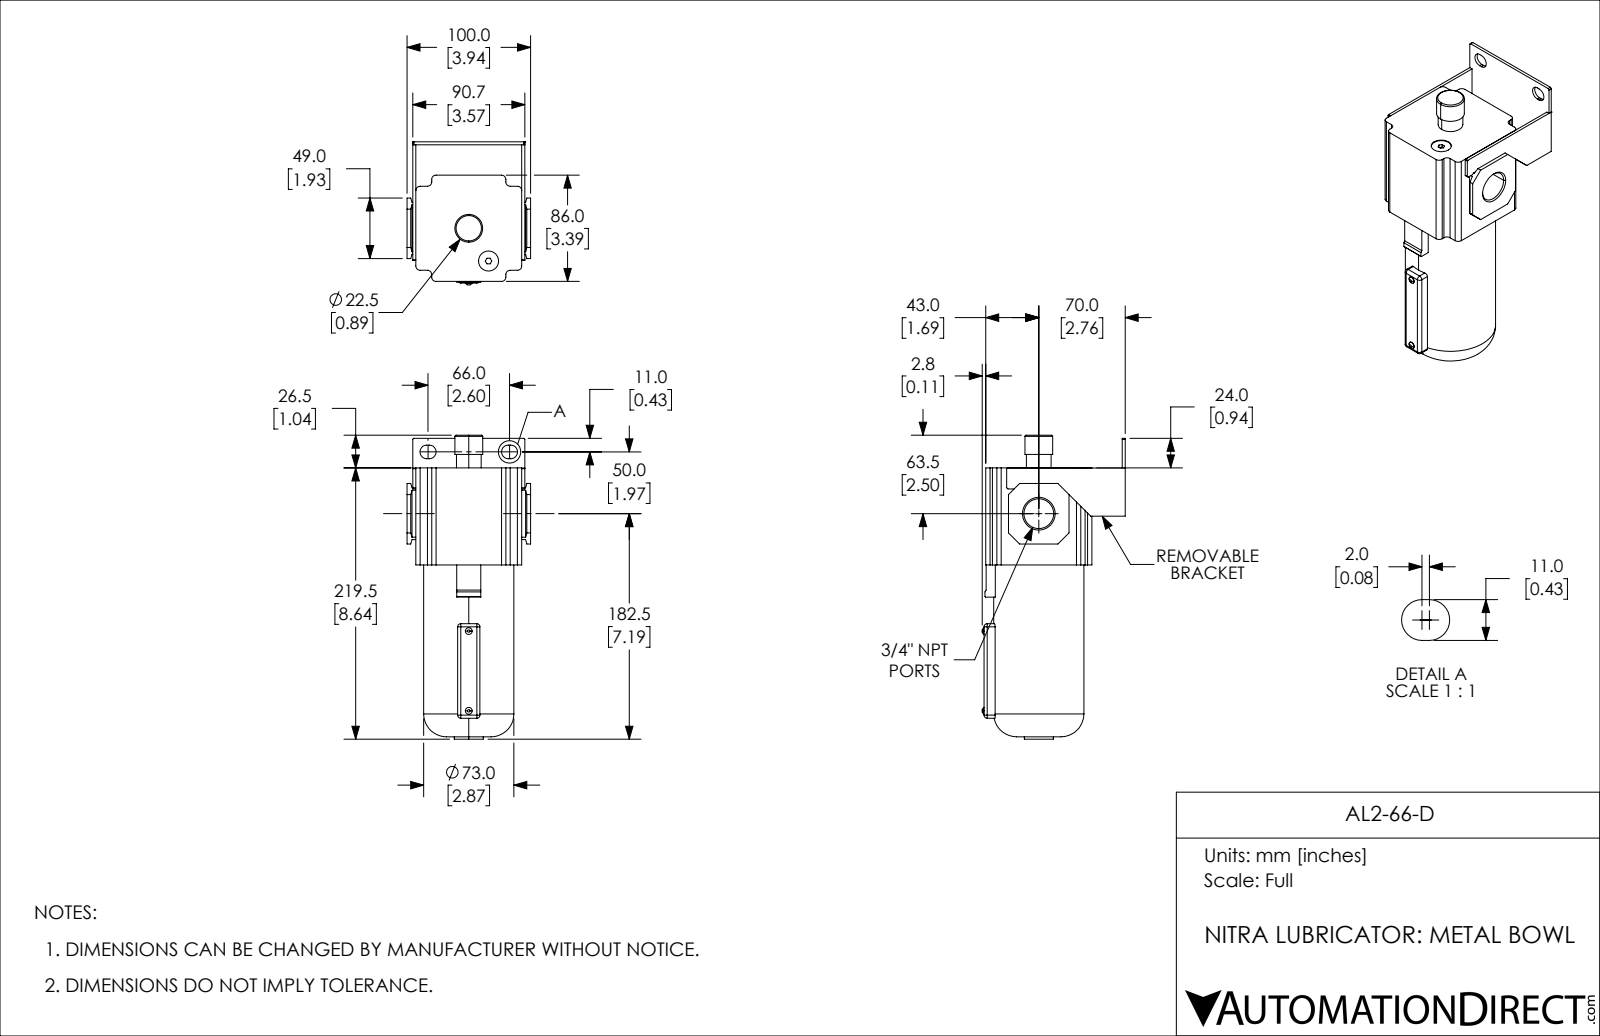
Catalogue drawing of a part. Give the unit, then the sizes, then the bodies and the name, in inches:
Units: inches
Overall size (bounding box): 9.685 × 4.559 × 3.937
Round holes (diameter × count): ⌀0.638 ×1, ⌀0.95 ×1
Round bosses / shafts (diameter × count): ⌀0.217 ×2, ⌀2.874 ×1, ⌀0.925 ×1, ⌀0.886 ×1, ⌀0.787 ×1
Partial cylindrical surfaces — rounded edges, fillets, slot ends (radius × count): R0.138 ×12, R0.098 ×8, R0.217 ×4, R0.039 ×2
Main face-to-face distances: 0.098, 3.472, 1.063, 0.965, 4.449, 3.386, 4.35, 3.374, 0.183, 0.281
Volume: 70.97 in³ · Surface area: 153.6 in²
Bodies: 1 solid, 162 faces (102 planar, 44 cylindrical, 16 other)
Part name (STEP PRODUCT): AL2-66-D
STEP written by: SolidWorks 2019 (CONFIG_CONTROL_DESIGN)
